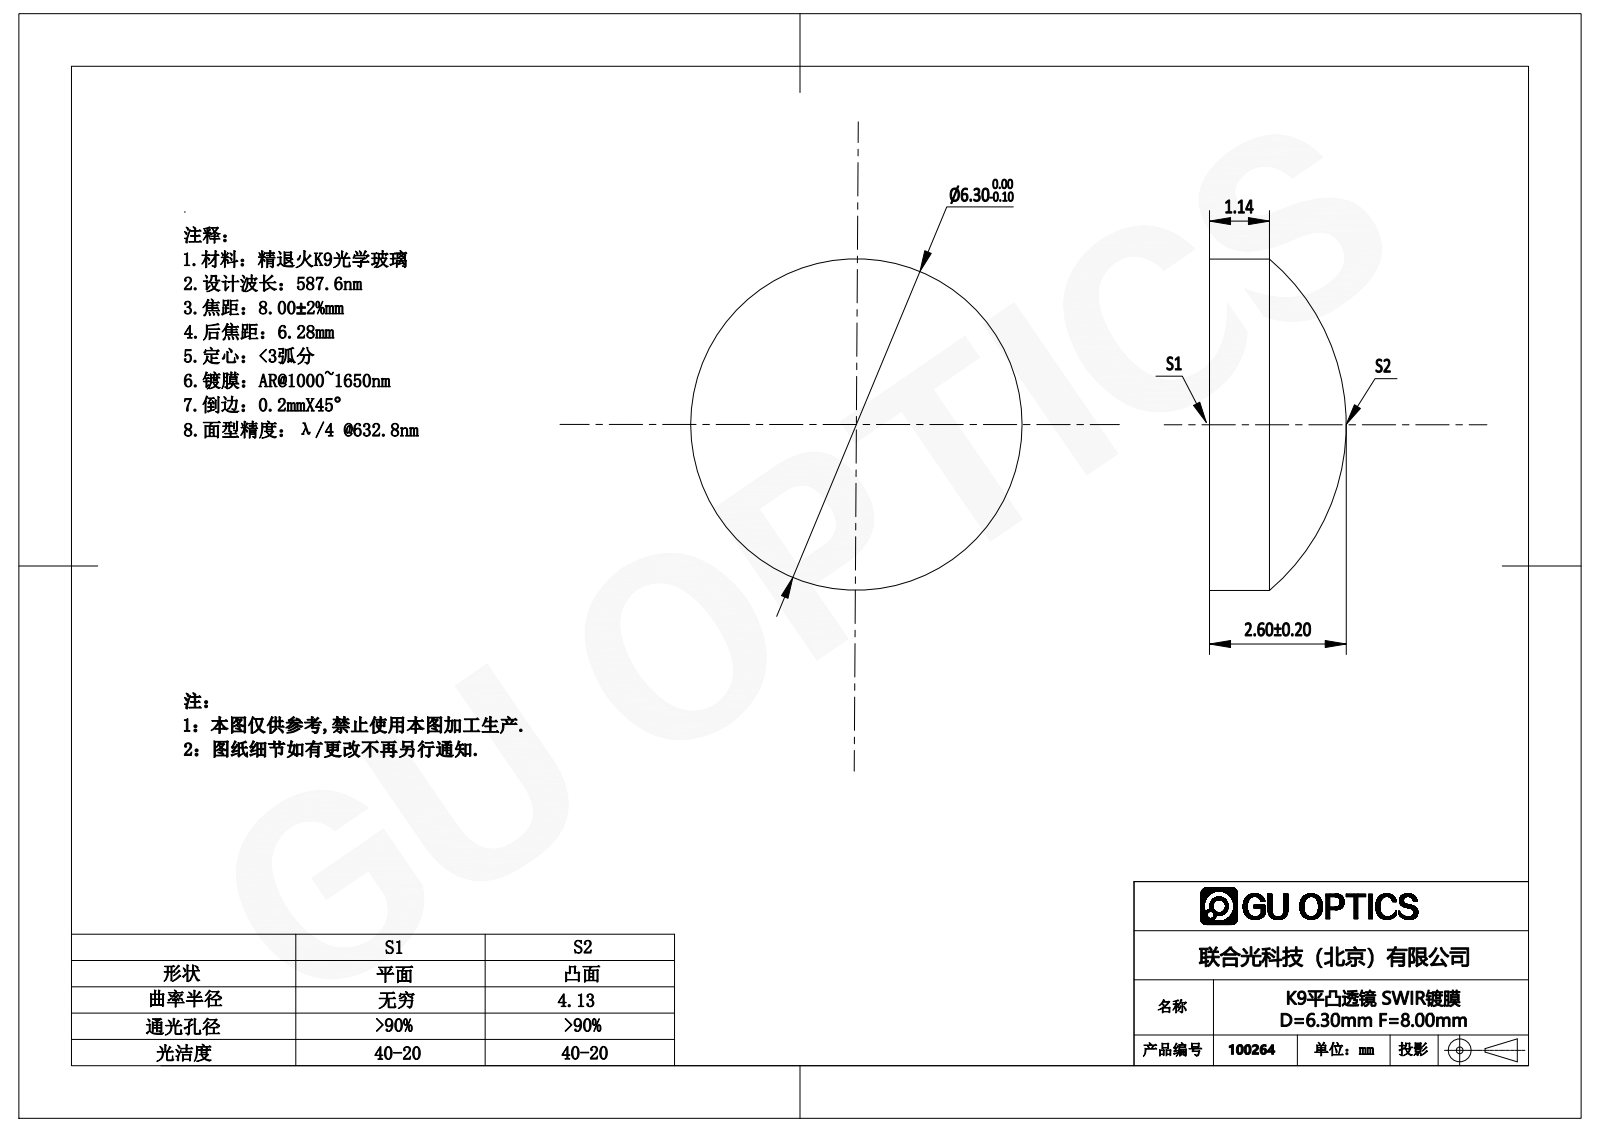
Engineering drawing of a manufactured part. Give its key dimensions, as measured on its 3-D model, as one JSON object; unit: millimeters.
{"part_name": "100092", "step_written_by": "SolidWorks 2016 (AUTOMOTIVE_DESIGN)", "units": "millimeters", "bodies": {"solids": 1, "faces": 5, "planar": 1, "cylindrical": 2, "other": 2}, "overall_size": [6.3, 6.3, 2.6], "volume_mm3": 60, "surface_area_mm2": 92, "round_bosses_or_shafts": [[6.3, 1]]}
